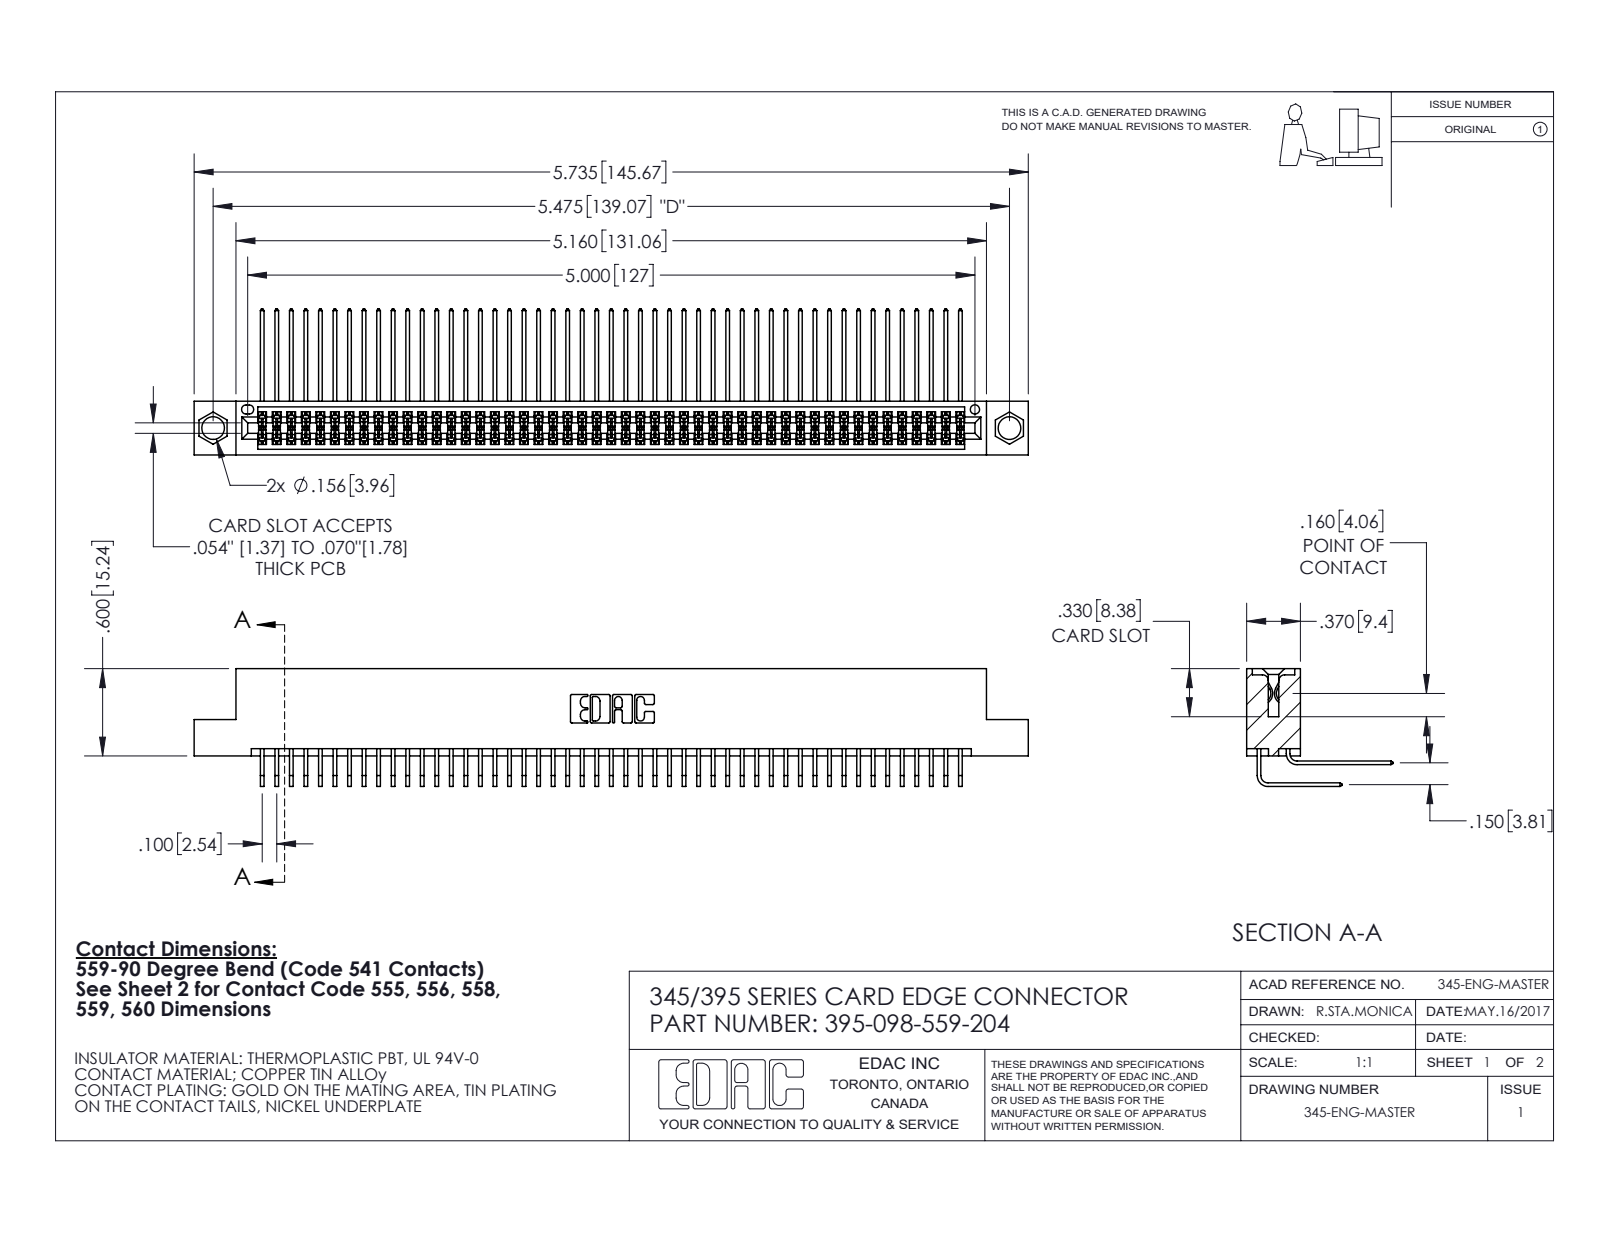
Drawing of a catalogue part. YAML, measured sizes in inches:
part_name: "345-292-001_558 559 Tail - 1; 395-098-559-204; 345-292-001_559 Tail - 2; 345 Part_Flush Mounting Lugs - 0.156 Dia-TI"
step_written_by: "SolidWorks 2020 (CONFIG_CONTROL_DESIGN)"
units: inches
bodies: {solids: 99, faces: 5236, planar: 3524, cylindrical: 1712, other: 0}
overall_size: [5.735, 1.005, 0.809]
volume: 0.896
surface_area: 37.72
round_holes:
  - {diameter: 0.156, count: 2}
  - {diameter: 0.064, count: 1}
partial_cylinders:
  - {radius: 0.006, count: 196}
  - {radius: 0.01, count: 22}
  - {radius: 0.007, count: 6}
  - {radius: 0.031, count: 6}
  - {radius: 0.026, count: 3}
  - {radius: 0.014, count: 2}
  - {radius: 0.019, count: 2}
  - {radius: 0.022, count: 2}
face_to_face_distances: [0.072, 0.298, 0.2, 0.37, 0.098, 0.272, 0.025, 0.225, 0.175, 0.15]
hole_center_spacings: [0.27, 5.239, 5.475]
